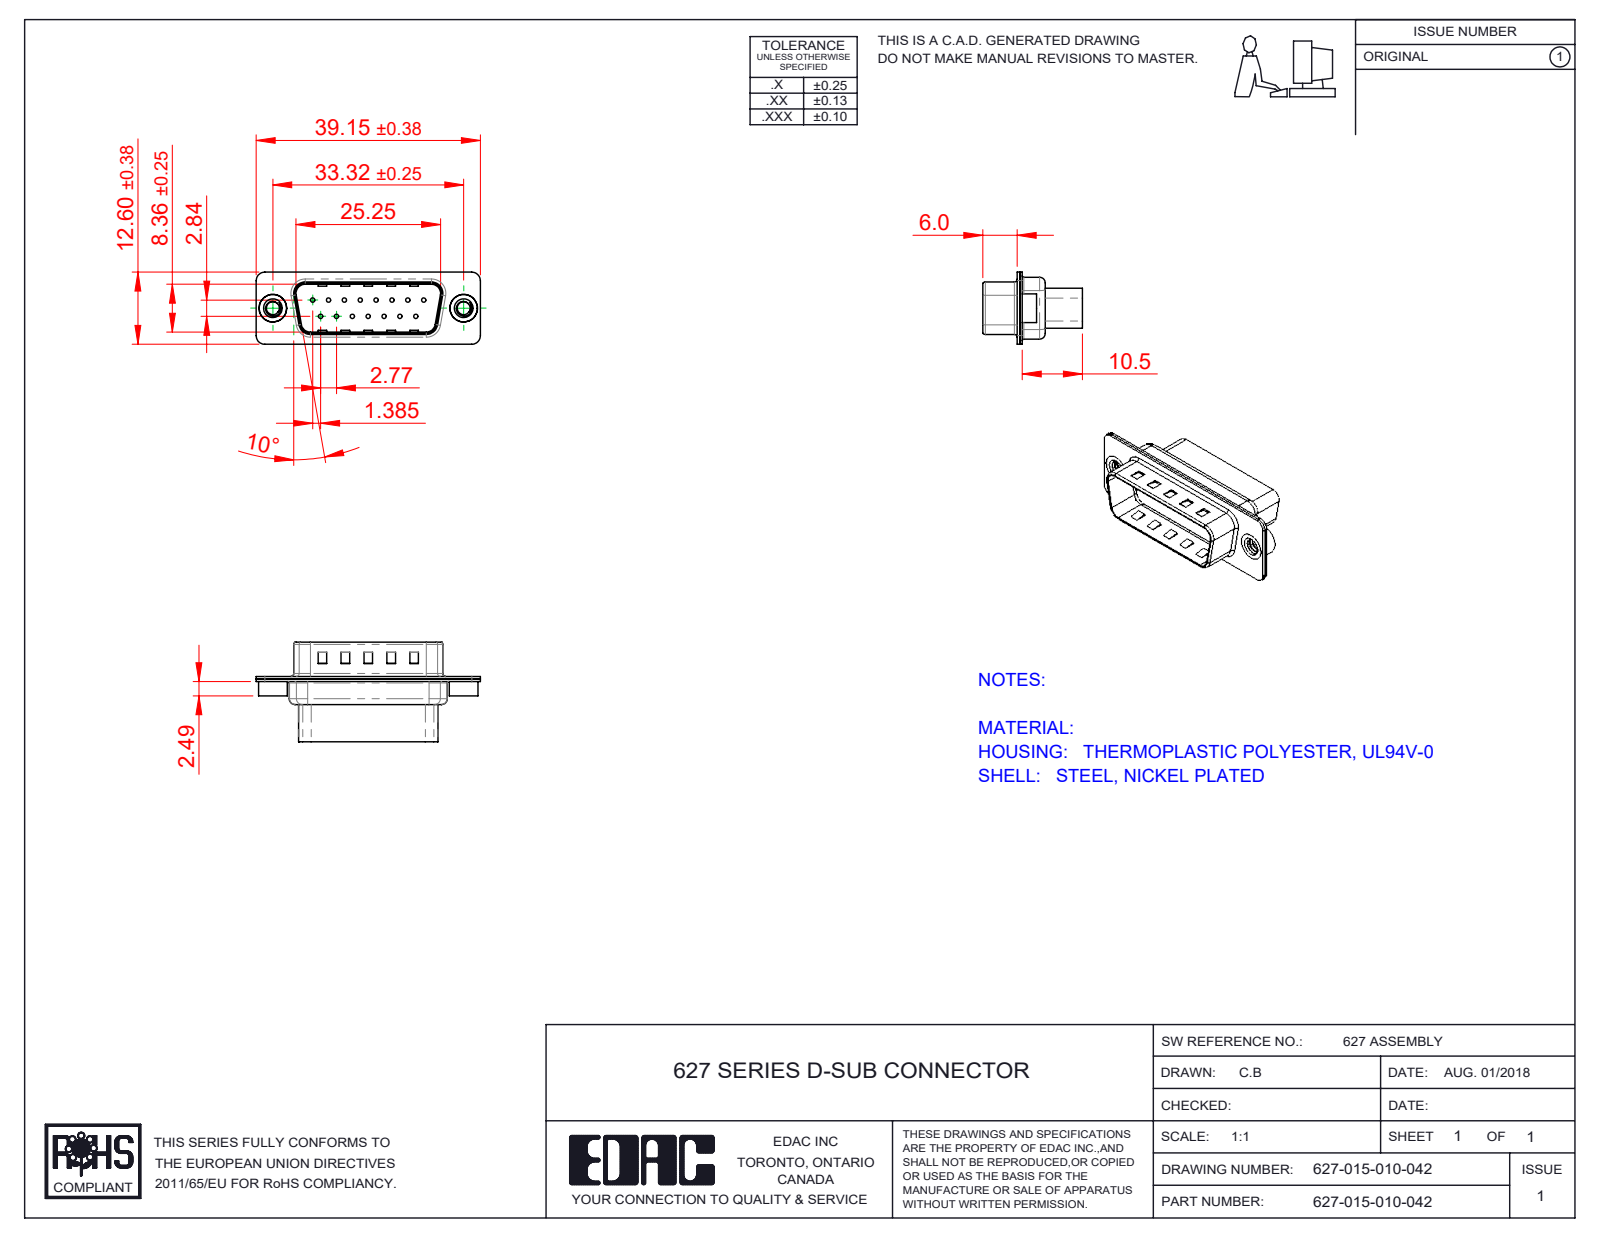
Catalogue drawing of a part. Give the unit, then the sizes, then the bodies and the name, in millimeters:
Units: millimetres
Overall size (bounding box): 39.15 × 17.4 × 12.6
Round holes (diameter × count): ⌀0.75 ×15, ⌀1.6 ×15, ⌀2 ×15, ⌀2.26 ×2, ⌀4 ×2, ⌀4.8 ×2
Round bosses / shafts (diameter × count): ⌀5 ×2, ⌀4.9 ×2
Partial cylindrical surfaces — rounded edges, fillets, slot ends (radius × count): R1.5 ×16, R2 ×12, R0.5 ×8, R1.6 ×8, R0.25 ×4, R0.6 ×4, R0.65 ×4, R0.9 ×4
Main face-to-face distances: 0.4, 0.45, 0.9, 0.82, 9.58, 0.68, 7.68, 1.08, 8.08, 8.76
Hole centre spacings: 3.16, 2.77, 5.54, 8.31, 11.08, 5.03, 5.04, 7.48
Volume: 2 359 mm³ · Surface area: 4 705 mm²
Bodies: 5 solids, 456 faces (169 planar, 221 cylindrical, 66 other)
Part name (STEP PRODUCT): 627-015-010-042; 627 Shell Rear_15 Contacts; 627 4-40 Threaded Rivet; 627 Housing_15 HP (+1 more)
STEP written by: SolidWorks 2020 (CONFIG_CONTROL_DESIGN)
